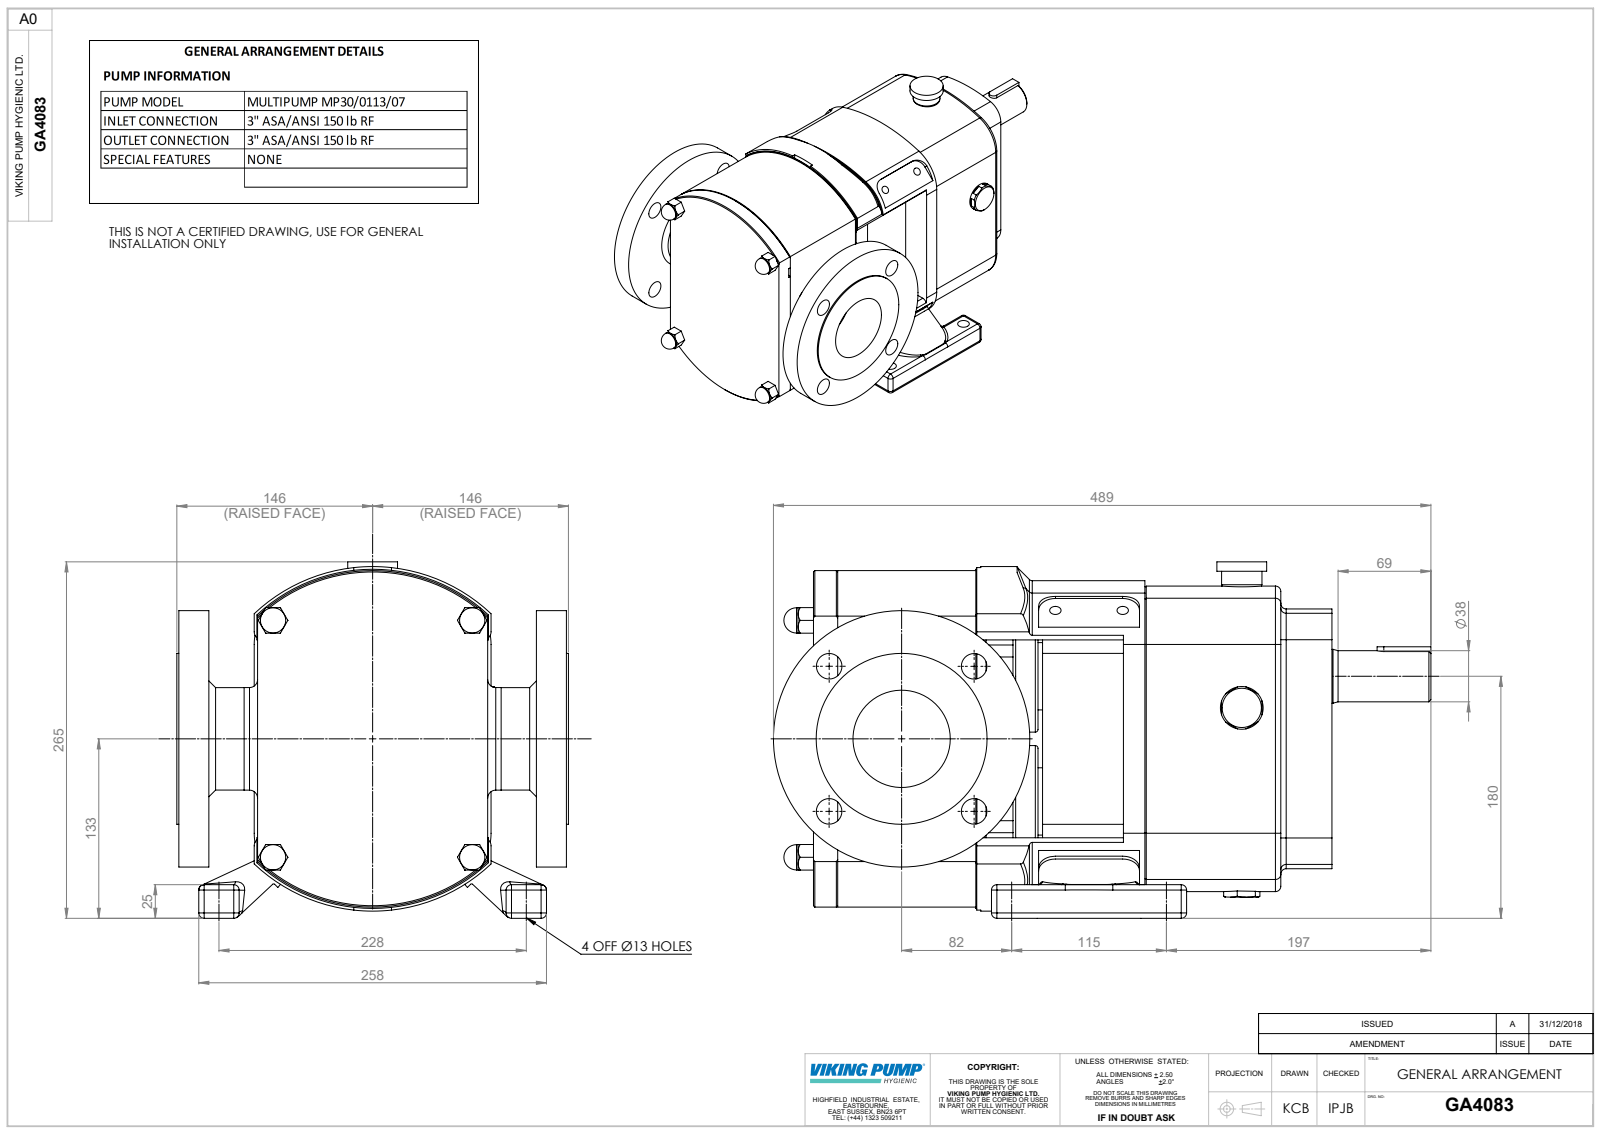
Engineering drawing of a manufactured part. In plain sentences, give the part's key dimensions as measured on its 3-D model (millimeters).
The part is named "Copy of Z94-5301-55 - 3 INCH ASA 150^GA4083; Copy of CP30-0113-07 H T^GA4083; GA4083". Its 3-D file was written by "SolidWorks 2023 (AUTOMOTIVE_DESIGN)". It is 3 solids with 727 faces: 267 planar, 257 cylindrical and 203 other. Overall it measures 488.58 by 291 by 264.84 millimeters. Its volume is 13 970 000 cubic millimeters and its surface area 694 218 square millimeters. Round holes: 6 of diameter 19, 4 of diameter 8.5, 4 of diameter 10.11, 4 of diameter 13, 2 of diameter 9.09, 1 of diameter 35, 1 of diameter 72.3. Round bosses or shafts: 4 of diameter 18.8, 2 of diameter 83, 2 of diameter 50, 1 of diameter 190.5, 1 of diameter 127, 1 of diameter 76.2, 1 of diameter 76.1, 1 of diameter 40.01. Partial cylindrical surfaces (rounded edges, fillets, slot ends): 44 of radius 4, 16 of radius 1, 12 of radius 10, 10 of radius 6, 4 of radius 12.5, 4 of radius 12.57, 4 of radius 12.6, 4 of radius 20. The main face-to-face distances are 229.5, 1.5, 60, 36.2, 207.2, 22.3, 58.5, 265.7, 228, 37.7. The hole center spacings are 76.2, 63.64, 107.76, 152.4, 161.59, 20.26, 50.05, 86.34.
